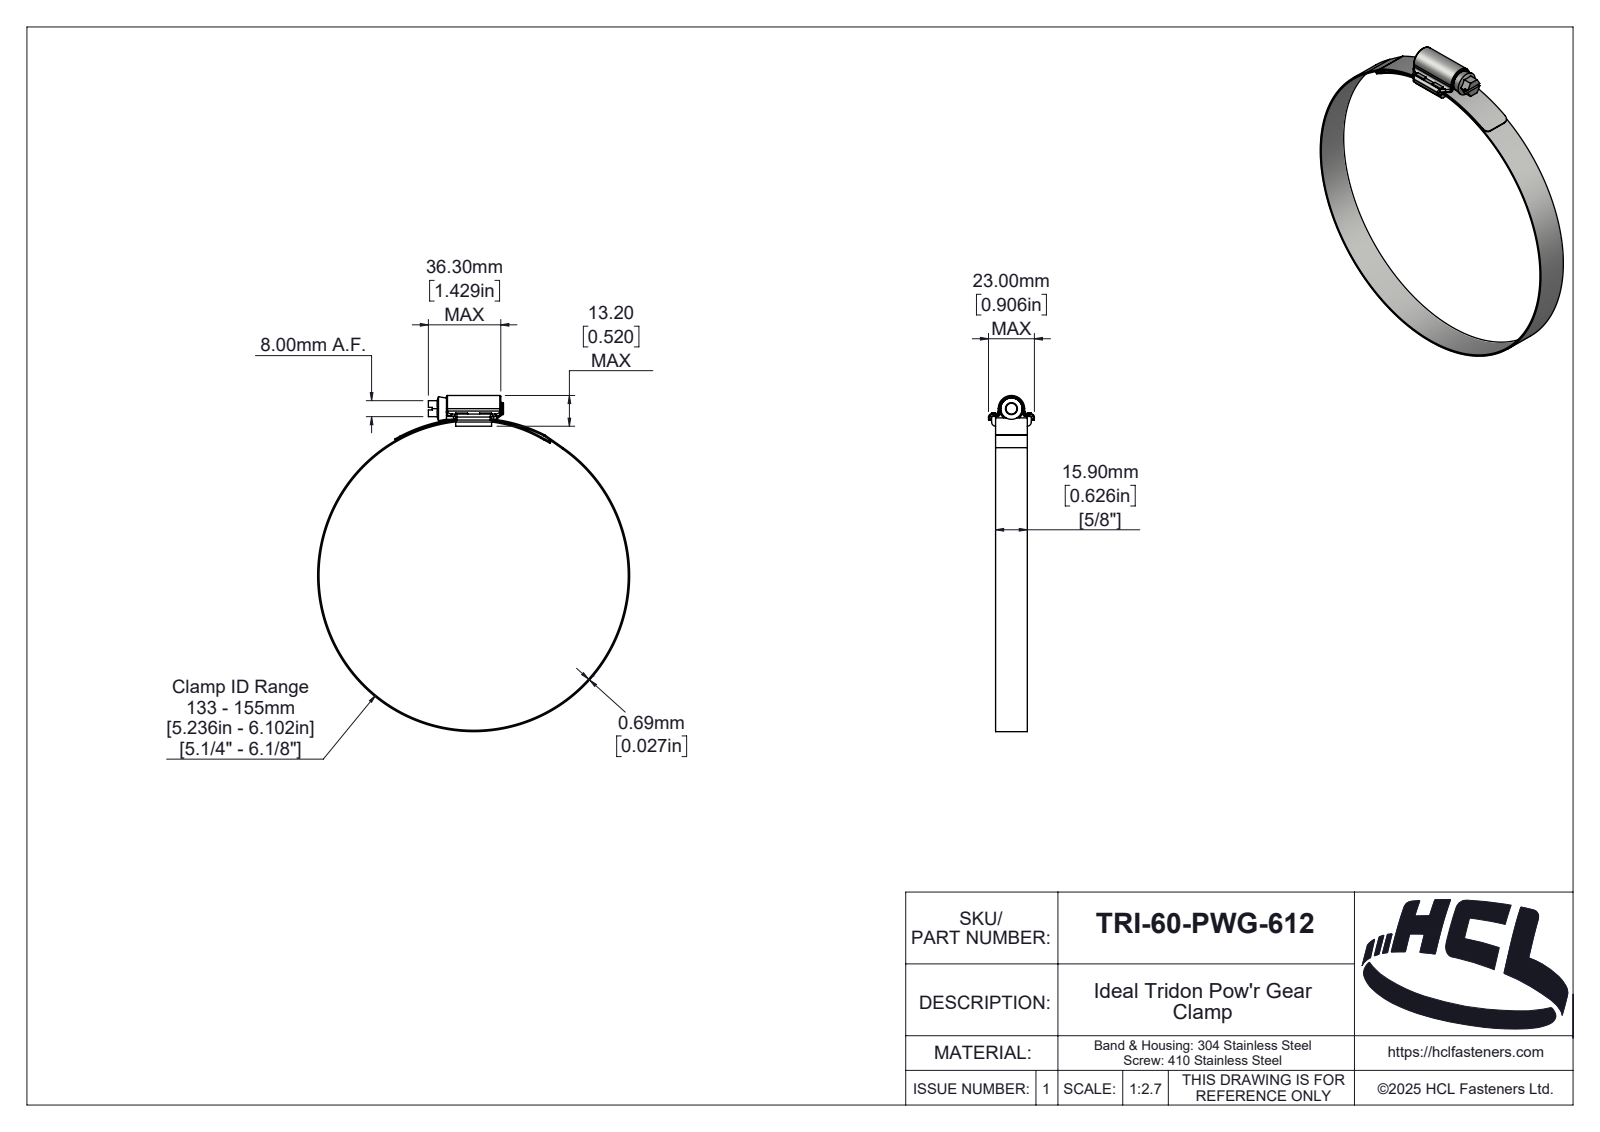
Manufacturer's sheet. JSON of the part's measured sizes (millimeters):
{"part_name": "TRI-60-PWG-612", "step_written_by": "SolidWorks 2025 (AUTOMOTIVE_DESIGN)", "units": "millimeters", "bodies": {"solids": 4, "faces": 268, "planar": 87, "cylindrical": 102, "other": 79}, "overall_size": [168.39, 156.38, 23], "volume_mm3": 11459, "surface_area_mm2": 23556, "round_holes": [[155, 1]], "round_bosses_or_shafts": [[156.38, 1], [10.7, 1], [6, 1]], "partial_cylinders_radius": [[1, 14], [0.5, 4], [1.5, 4], [2, 3], [0.1, 2], [2.1, 2], [3, 2], [0.46, 1]], "face_to_face_distances": [15.9, 2, 17.9, 0.69, 4.9, 1.2, 4.55, 3.35, 15.35, 2.55]}
